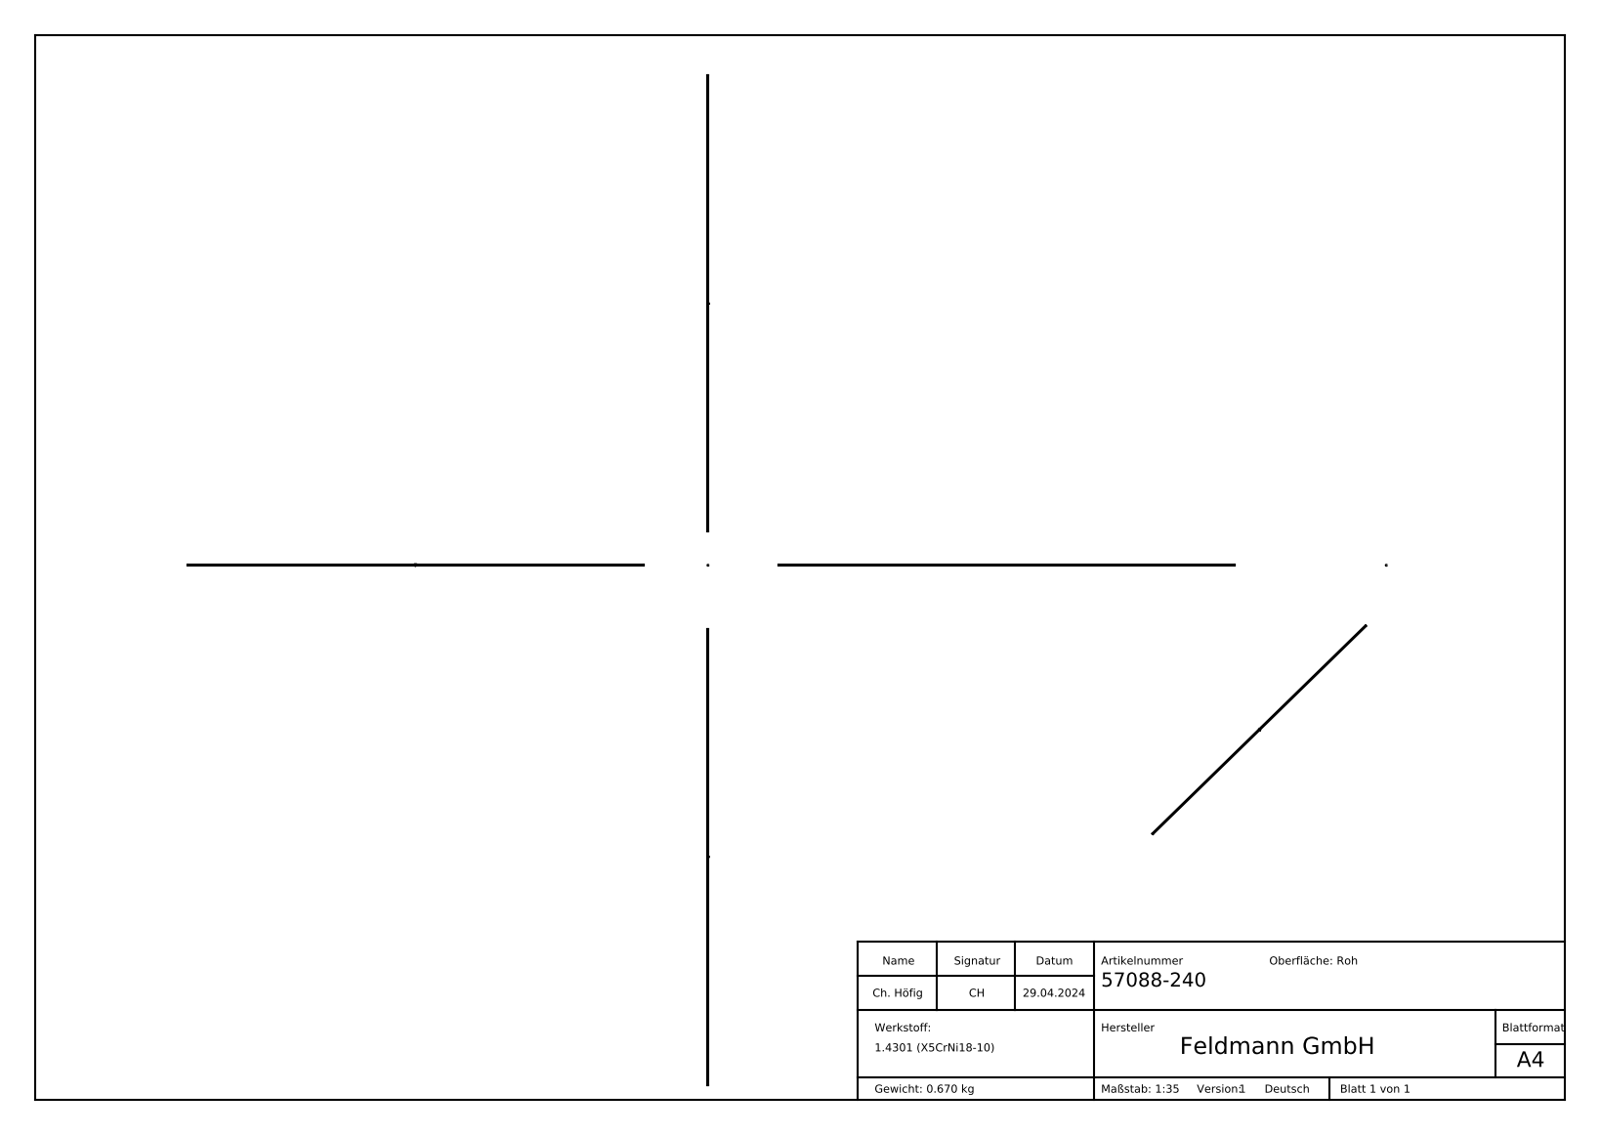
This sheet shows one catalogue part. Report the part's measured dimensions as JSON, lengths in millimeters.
{"part_name": "57088-240", "step_written_by": "SolidWorks 2018 (CONFIG_CONTROL_DESIGN)", "units": "millimeters", "bodies": {"solids": 1, "faces": 284, "planar": 105, "cylindrical": 35, "other": 144}, "overall_size": [3000, 6, 6], "volume_mm3": 84823, "surface_area_mm2": 56612, "round_bosses_or_shafts": [[6, 1]], "partial_cylinders_radius": [[2.9, 1]], "face_to_face_distances": [3000, 1.21, 2.04, 3.17, 2.41, 0.76, 1.13, 1.28, 0.83, 1.94]}
